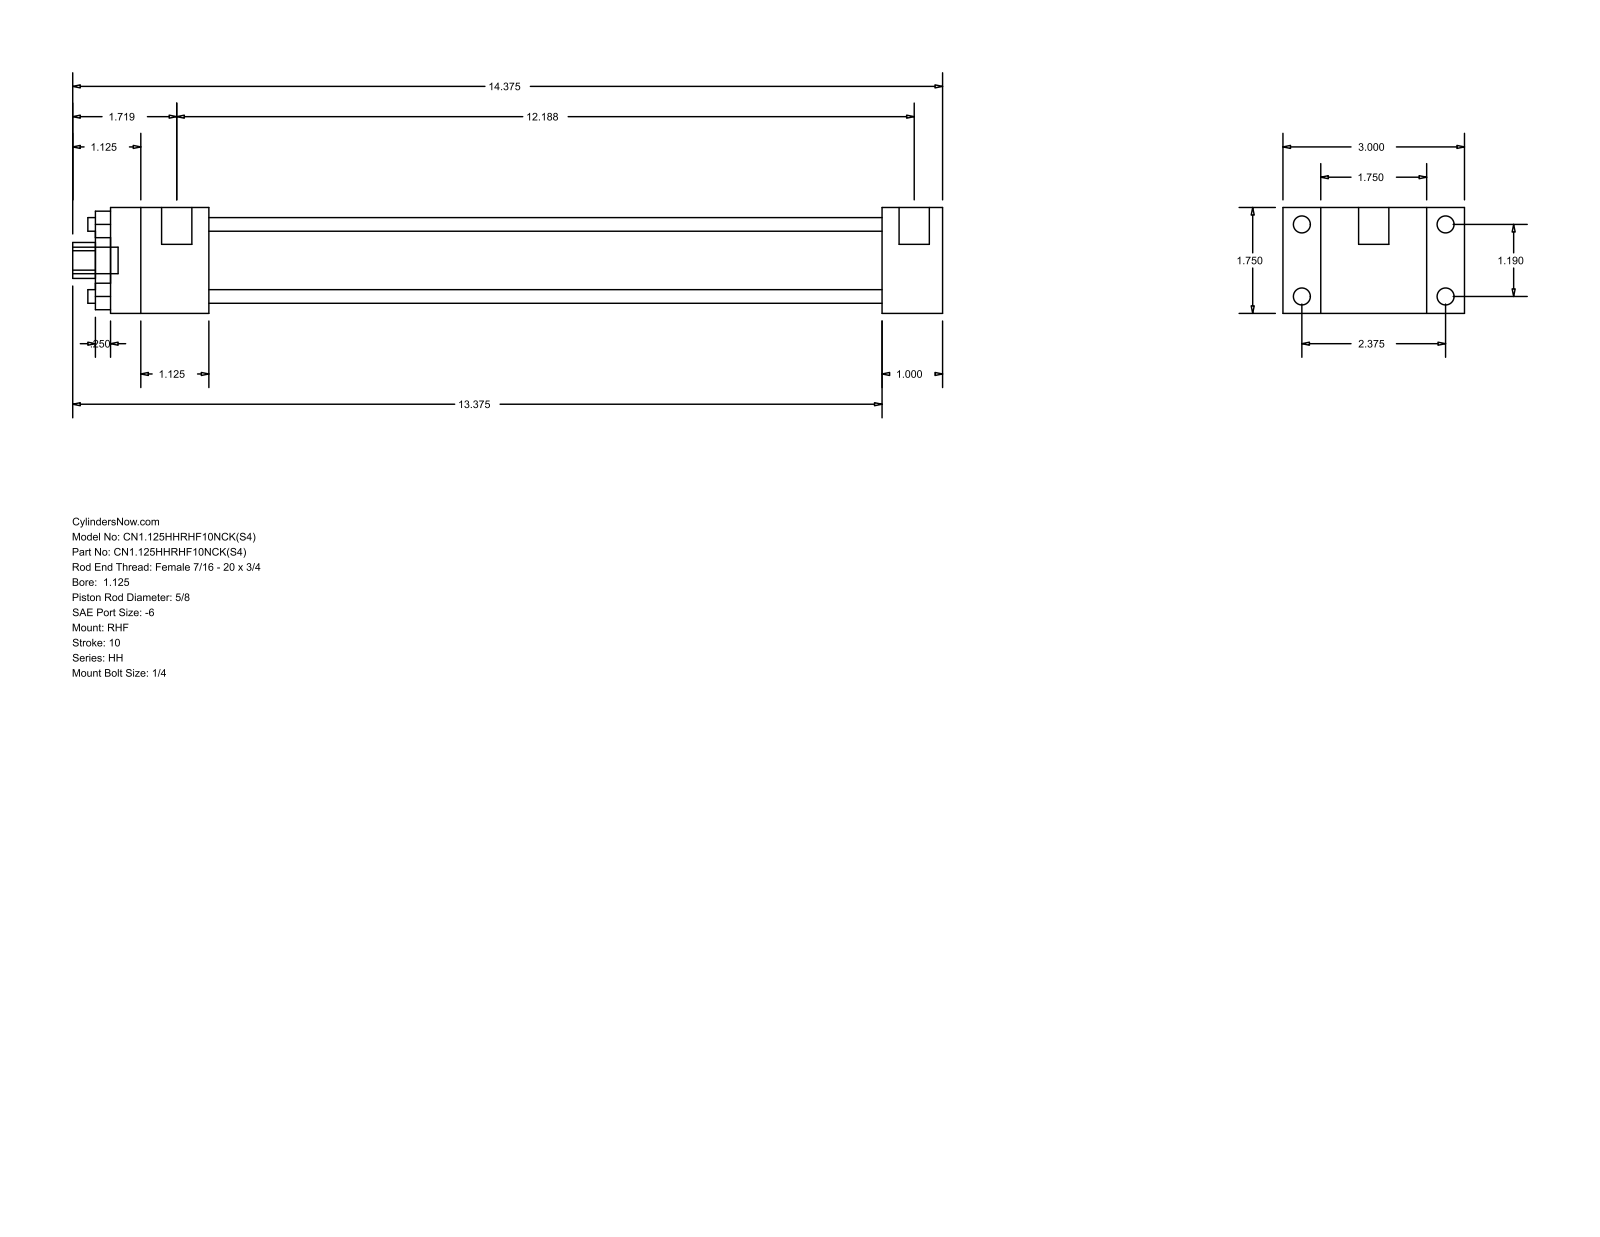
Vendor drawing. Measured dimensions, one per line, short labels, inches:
name: HH_RHF__0112_0.625
written by: GSSL Pune (CONFIG_CONTROL_DESIGN)
unit: in
bodies: 0 solids, 88 faces (60 planar, 28 cylindrical, 0 other)
size: 14.375 × 3 × 1.75
holes: 4× ⌀0.225, 1× ⌀0.625, 1× ⌀1.125, 1× ⌀1.375
bosses: 4× ⌀0.281, 4× ⌀0.219, 2× ⌀0.5, 1× ⌀0.437
rounds: 1× R0.297
face distances: 1.75, 0.625, 2.375, 1, 3, 11.125, 12.125, 1.625, 12.75, 13.75
hole spacings: 0.841, 1.19, 1.683
